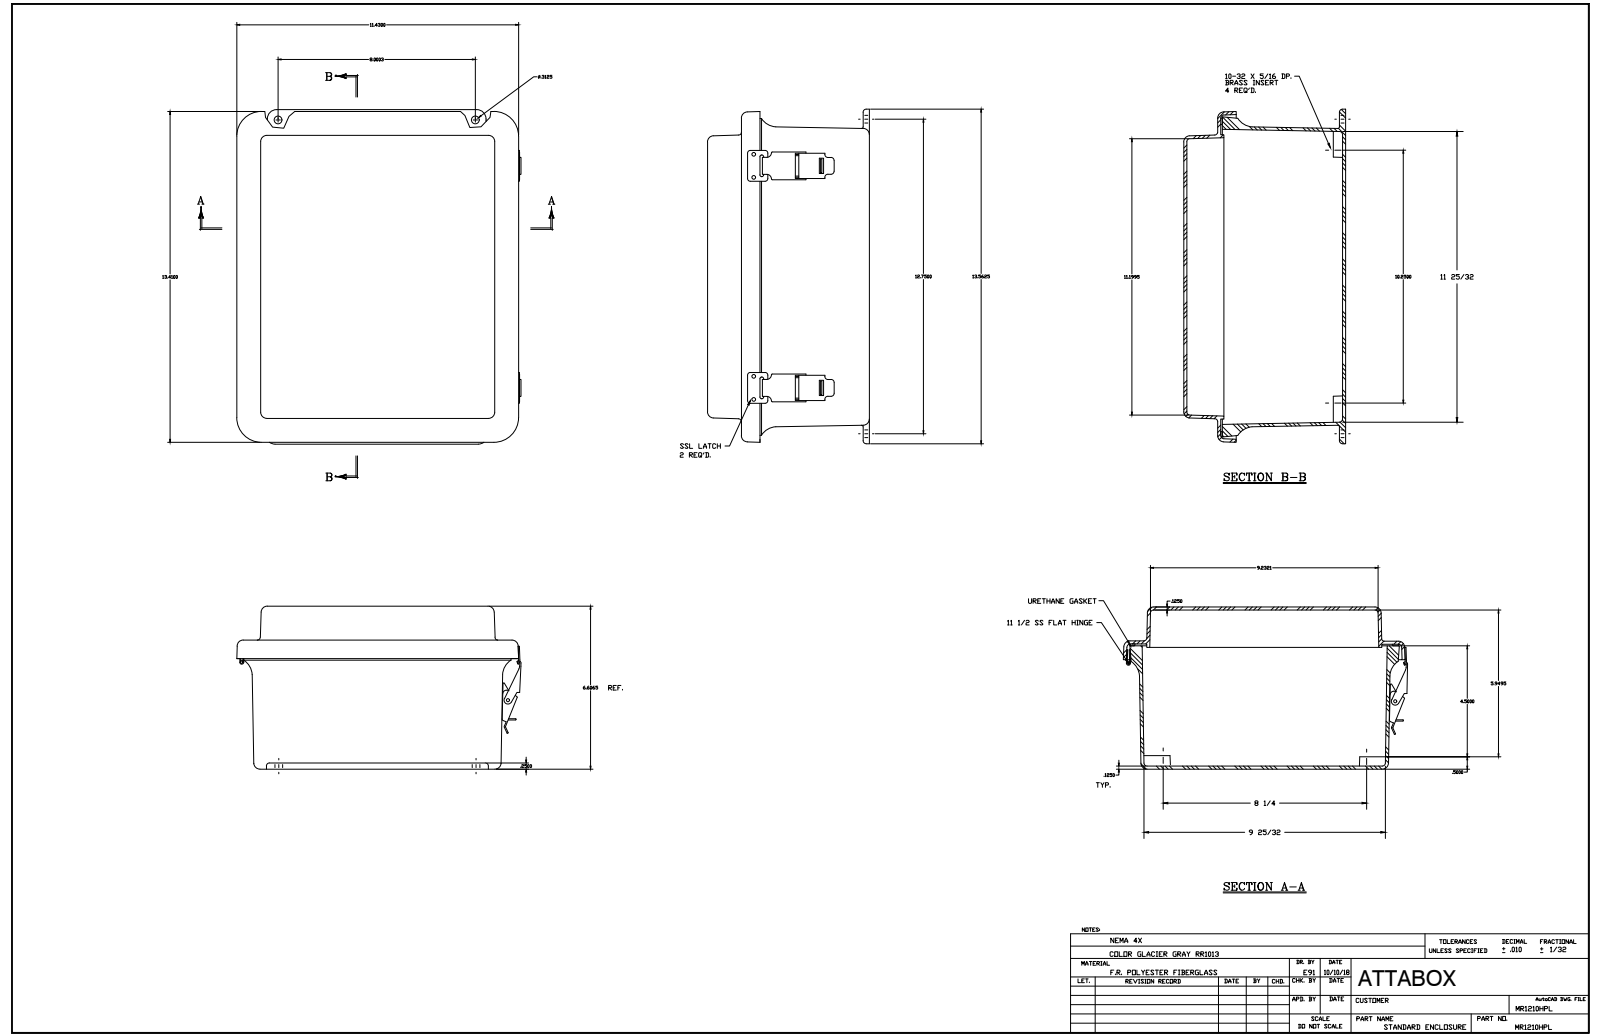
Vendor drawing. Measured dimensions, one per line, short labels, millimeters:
name: MR1210HPL
written by: SolidWorks 2018 (AUTOMOTIVE_DESIGN)
unit: mm
bodies: 38 solids, 1046 faces (446 planar, 429 cylindrical, 171 other)
size: 344.5 × 293 × 167.3
volume: 1 511 000 mm³; area: 844 500 mm²
holes: 20× ⌀3.6, 8× ⌀2.6, 8× ⌀3.3, 5× ⌀3.9, 4× ⌀3.3, 4× ⌀4, 4× ⌀5.5, 2× ⌀3.4, 2× ⌀9.5, 1× ⌀2.2, 1× ⌀2.2, 1× ⌀3.4
bosses: 11× ⌀3.2, 8× ⌀6.4, 5× ⌀3.2, 4× ⌀6.9, 1× ⌀7.6, 1× ⌀4.3, 1× ⌀3.9, 1× ⌀3.9
rounds: 28× R3.2, 20× R0.4, 20× R0.8, 16× R1.1, 12× R0.8, 12× R6.4, 9× R0.6, 6× R1.5
face distances: 3.2, 164.2, 167.3, 161, 128.9, 35.2, 125.7, 38.4, 132.1, 32.1
hole spacings: 228.6, 229.4, 23.8, 19.1, 92.1, 6.4, 19.1, 34.2
